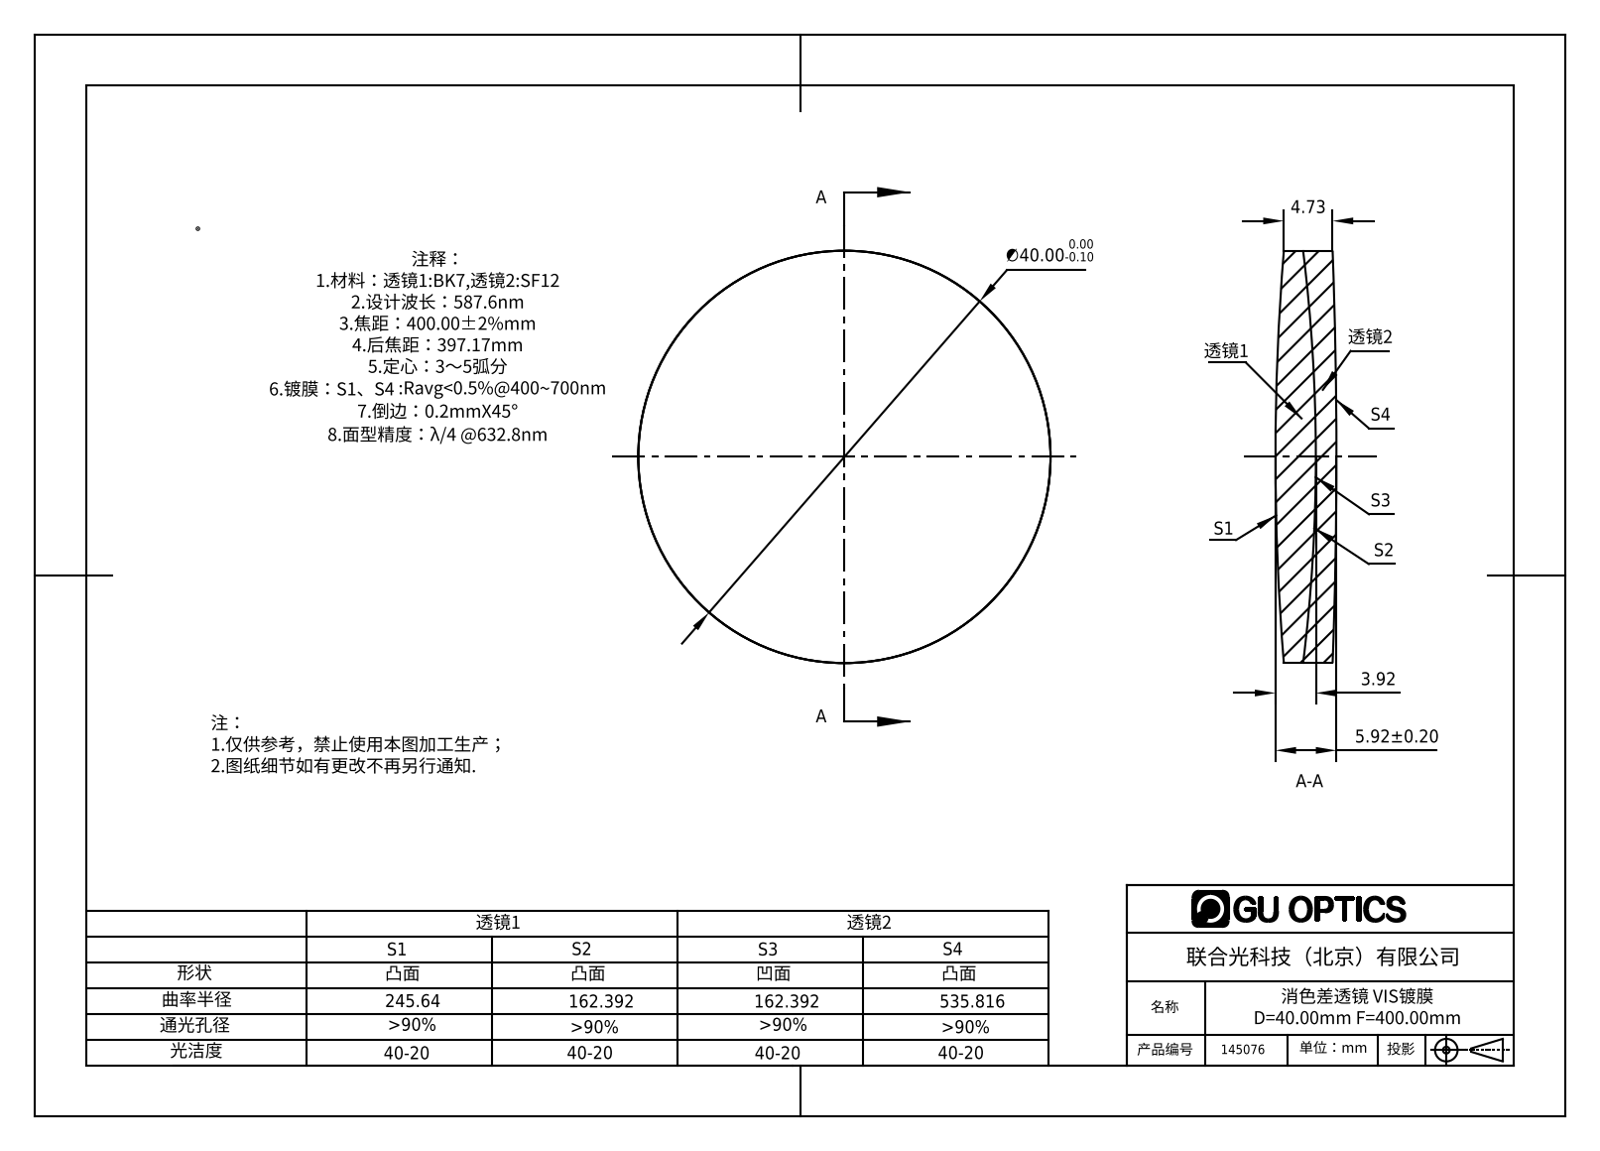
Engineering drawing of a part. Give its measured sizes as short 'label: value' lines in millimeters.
name: 145076
written by: SolidWorks 2016 (AUTOMOTIVE_DESIGN)
unit: mm
bodies: 2 solids, 12 faces (0 planar, 4 cylindrical, 8 other)
size: 40 × 40 × 5.92
volume: 6 693 mm³; area: 5 633 mm²
bosses: 1× ⌀40
